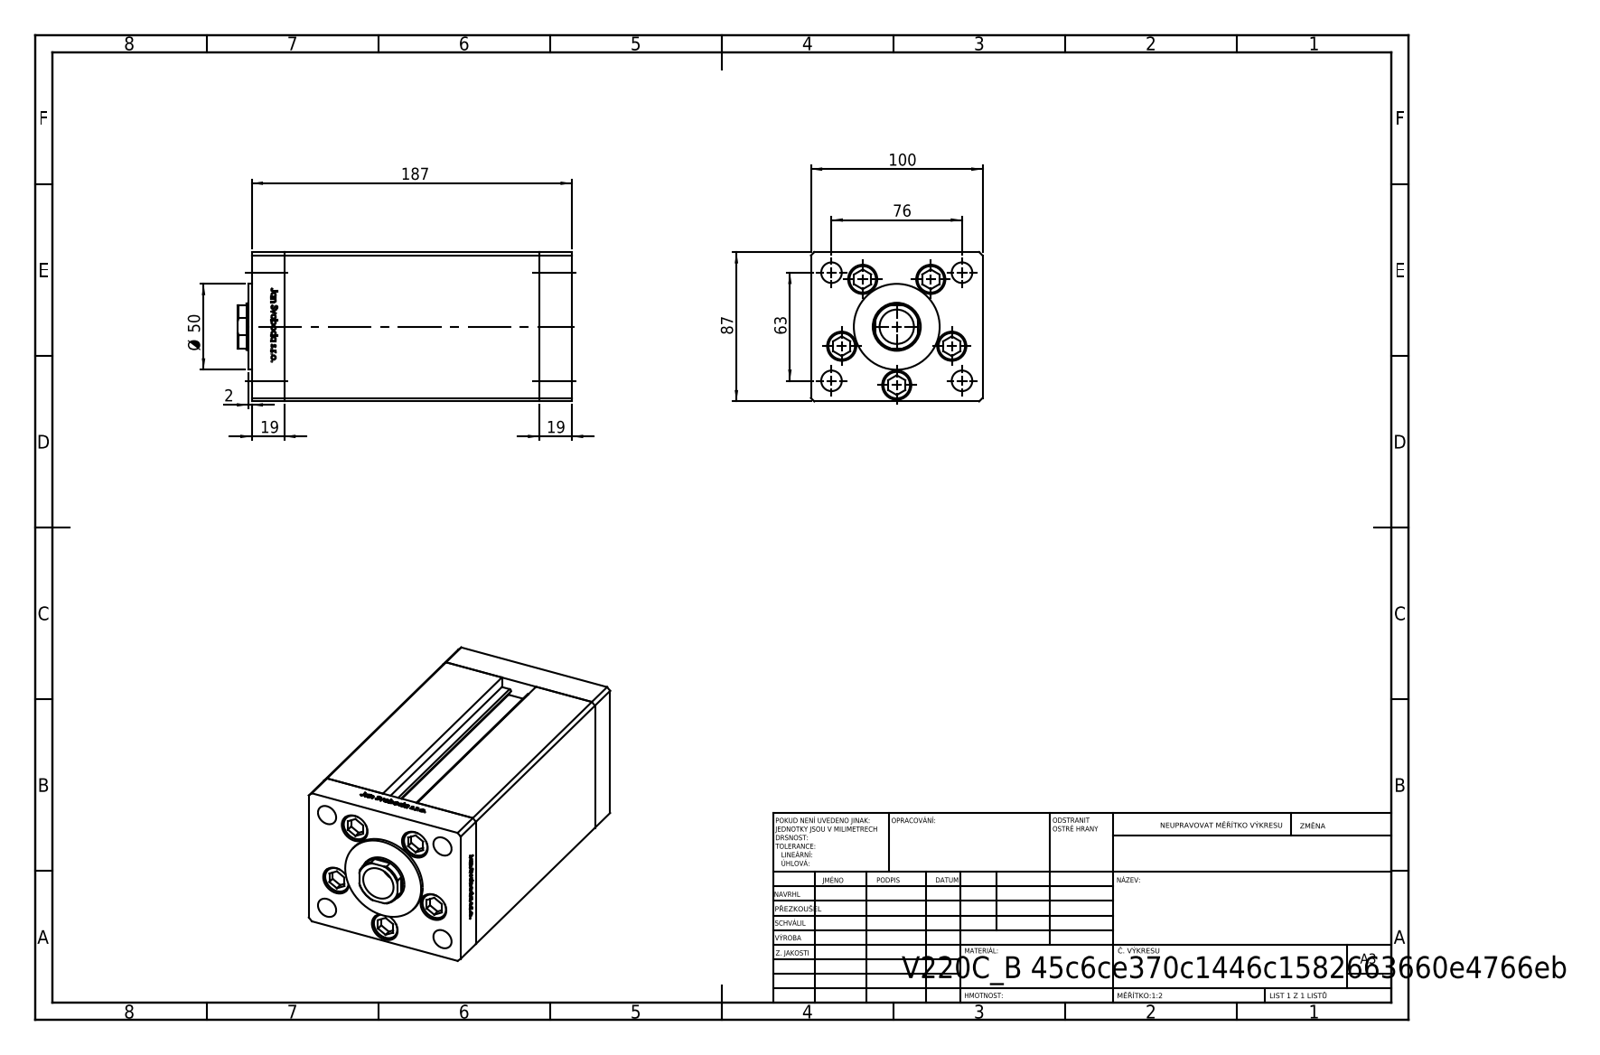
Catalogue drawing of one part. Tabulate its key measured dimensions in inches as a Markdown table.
| quantity | value |
| --- | --- |
| part name | V220C_B_VC; V220C BACK_B; ALLEN BOLT; V220C_B MIDDLE (+1 more) |
| STEP written by | SolidWorks 2019 (CONFIG_CONTROL_DESIGN) |
| units | inches |
| bodies | 14 solids, 1175 faces (460 planar, 143 cylindrical, 572 other) |
| overall size | 7.657 × 3.937 × 3.425 |
| volume | 87.39 in³ |
| surface area | 311.5 in² |
| round holes (diameter × count) | 0.531 × 7, 0.669 × 5, 0.472 × 4, 0.079 × 2, 0.518 × 2, 0.787 × 1, 1.102 × 1 |
| round bosses / shafts (diameter × count) | 0.315 × 5, 0.669 × 2, 1.969 × 1 |
| partial cylindrical surfaces (radius × count) | 0.037 × 2, 0.531 × 1 |
| main face-to-face distances | 3.937, 3.425, 5.846, 0.748, 6.594, 7.343, 0.354, 0.394, 6.988, 6.24 |
| hole center spacings | 1.339, 0.732, 1.561, 1.943, 2.281, 0.828, 1.499, 1.546 |
